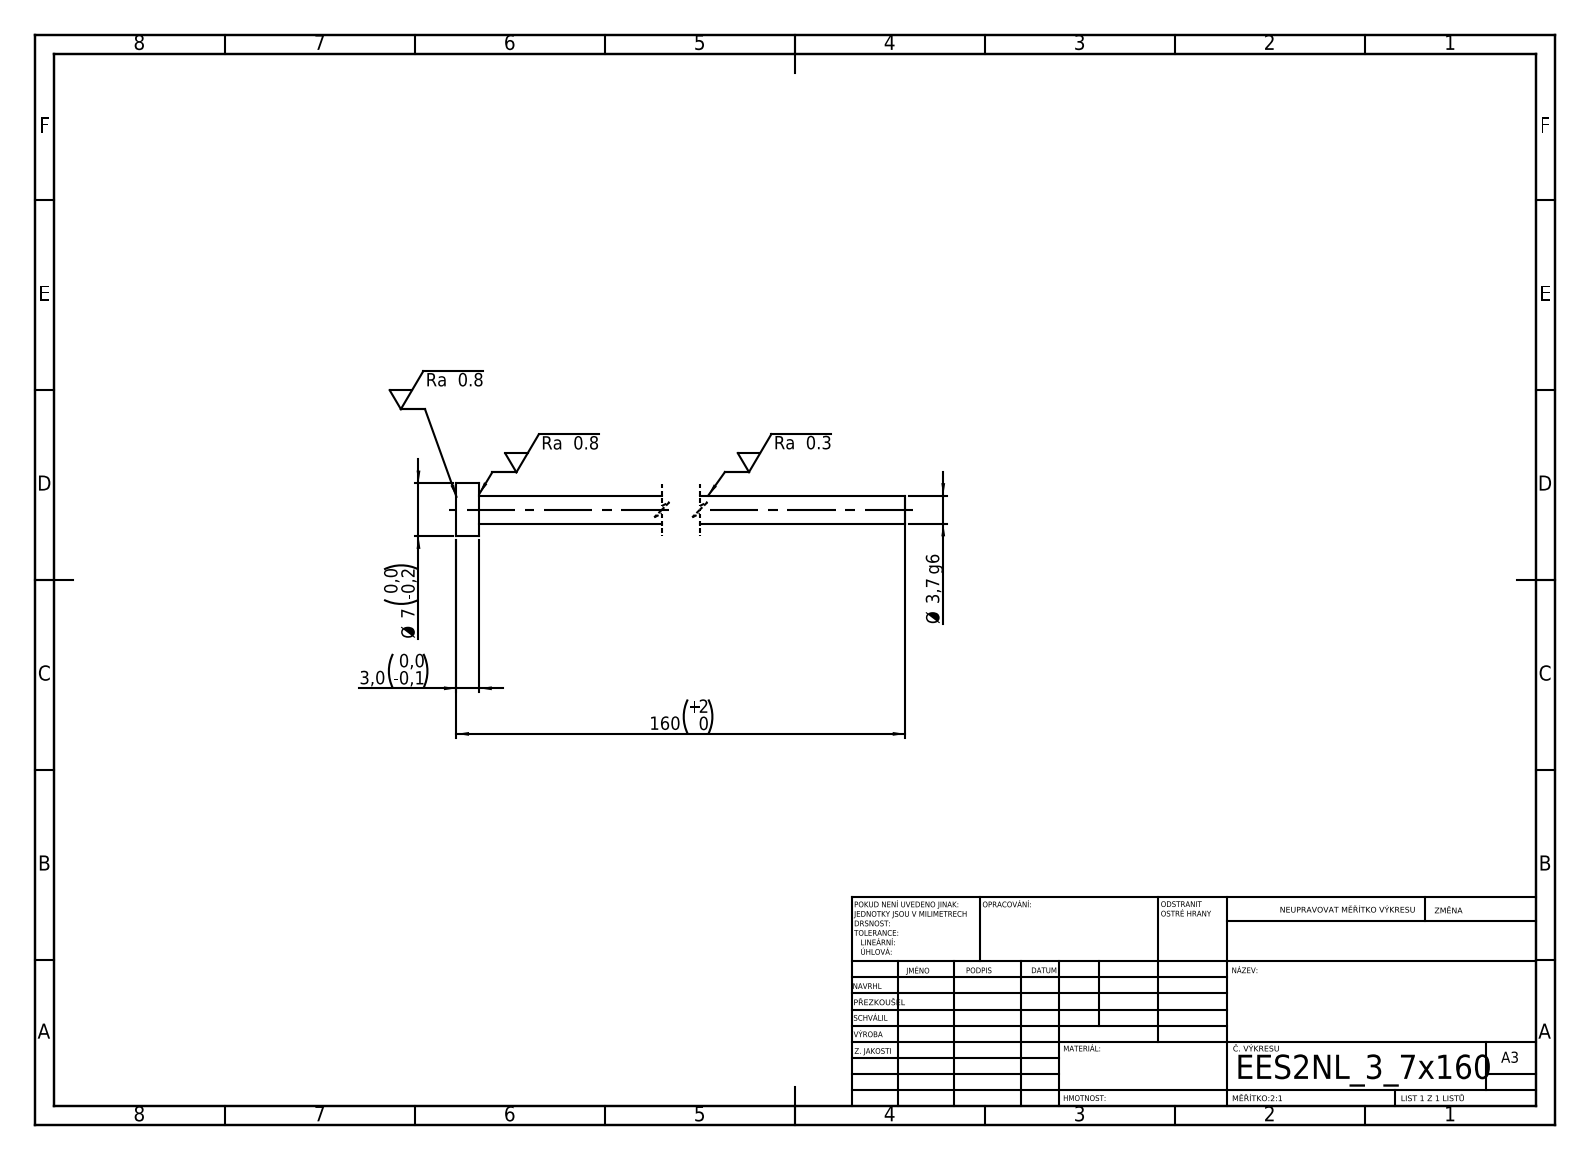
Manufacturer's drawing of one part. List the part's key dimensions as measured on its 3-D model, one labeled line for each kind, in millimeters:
STEP written by: SolidWorks 2019 (CONFIG_CONTROL_DESIGN)
Units: millimetres
Bodies: 1 solid, 7 faces (3 planar, 4 cylindrical, 0 other)
Overall size (bounding box): 160 × 7 × 7
Volume: 1 804 mm³ · Surface area: 1 968 mm²
Round bosses / shafts (diameter × count): ⌀7 ×1, ⌀3.7 ×1
Main face-to-face distances: 3, 160, 157
